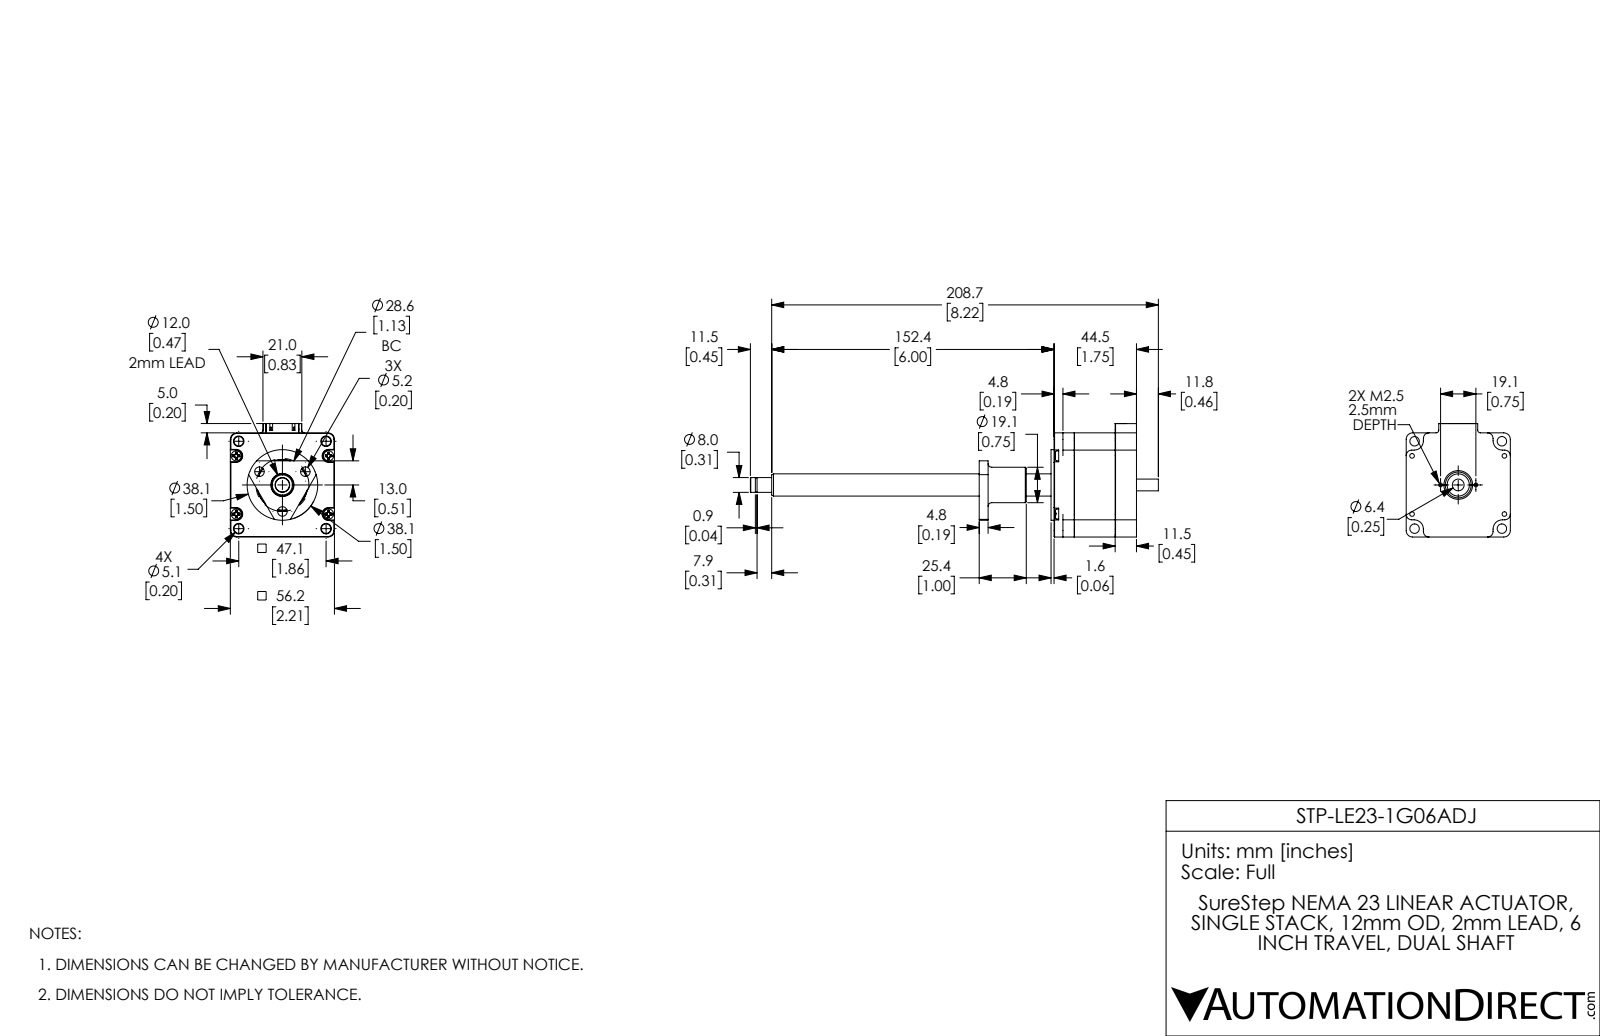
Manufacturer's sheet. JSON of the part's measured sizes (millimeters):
{"part_name": "STP-LE23-1G06ADJ; STP-LE23-1G06ADJ_1; STP-LE23-1G06ADJ_2", "step_written_by": "SolidWorks 2017 (AUTOMOTIVE_DESIGN)", "units": "millimeters", "bodies": {"solids": 8, "faces": 751, "planar": 306, "cylindrical": 205, "other": 240}, "overall_size": [220.2, 61.22, 56.2], "volume_mm3": 125176, "surface_area_mm2": 50699, "round_holes": [[4.5, 8], [2.5, 4], [3.3, 4], [5.1, 4], [5.16, 3], [2, 2], [2.05, 2], [6.8, 1], [10.5, 1], [15.5, 1], [20, 1], [24, 1]], "round_bosses_or_shafts": [[5.4, 4], [38.1, 1], [36, 1], [35.6, 1], [34.85, 1], [19.1, 1], [16, 1], [12, 1]], "partial_cylinders_radius": [[1.5, 10], [3, 8], [1.8, 4], [3.2, 4], [3.5, 4], [5, 4], [19.3, 1]], "face_to_face_distances": [22, 44.5, 56.2, 11.5, 33.5, 1.6, 51.4, 11, 33, 38.8], "hole_center_spacings": [14.12, 24.75, 33.05, 35.01, 45.74, 48.53, 56.99, 6.55]}
